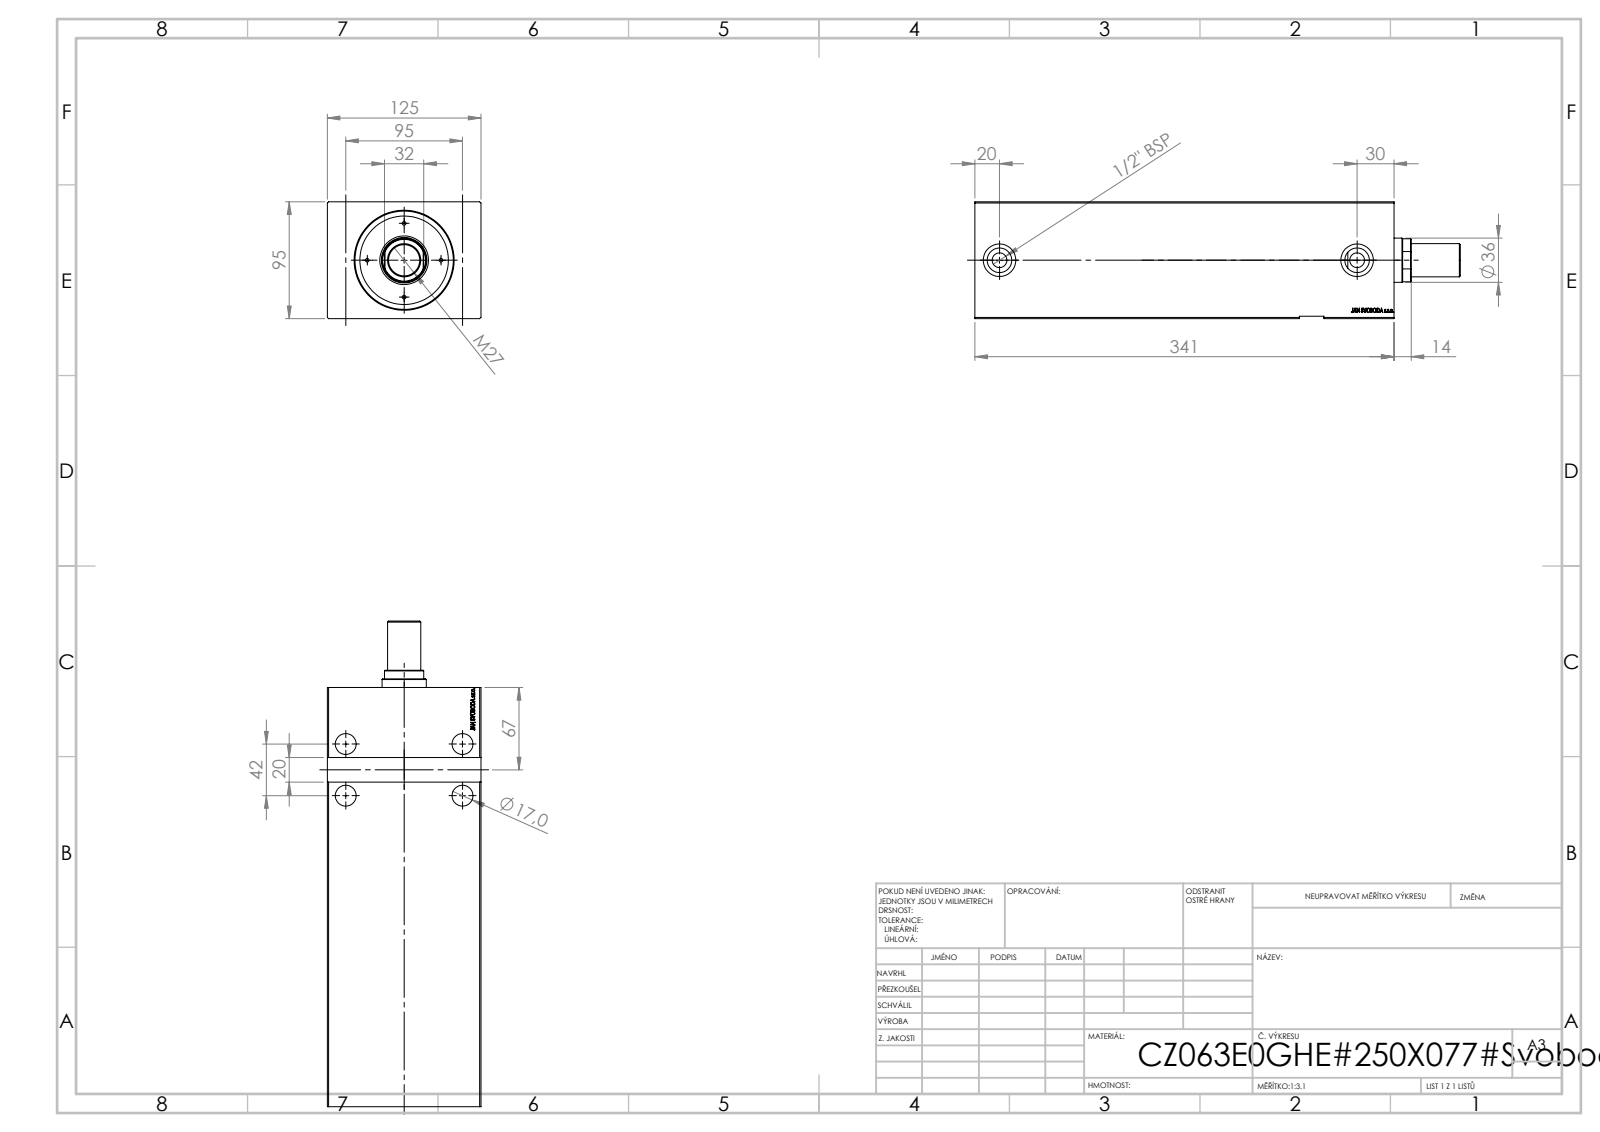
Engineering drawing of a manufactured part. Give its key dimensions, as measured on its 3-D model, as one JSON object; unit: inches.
{"step_written_by": "SolidWorks 2019 (CONFIG_CONTROL_DESIGN)", "units": "inches", "bodies": {"solids": 1, "faces": 807, "planar": 395, "cylindrical": 30, "other": 382}, "overall_size": [13.425, 4.921, 3.74], "volume_in3": 178.3, "surface_area_in2": 400.4, "round_holes": [[0.669, 4], [0.315, 2], [0.472, 2], [0.787, 2], [1.043, 2], [1.417, 1], [2.48, 1], [3.15, 1]], "face_to_face_distances": [3.74, 4.921, 13.425, 12.606, 0.819, 0.079, 3.661, 0.551, 12.055, 12.874], "hole_center_spacings": [1.654, 3.74, 4.089, 1.089, 2.168, 2.687, 3.277, 8.844]}
